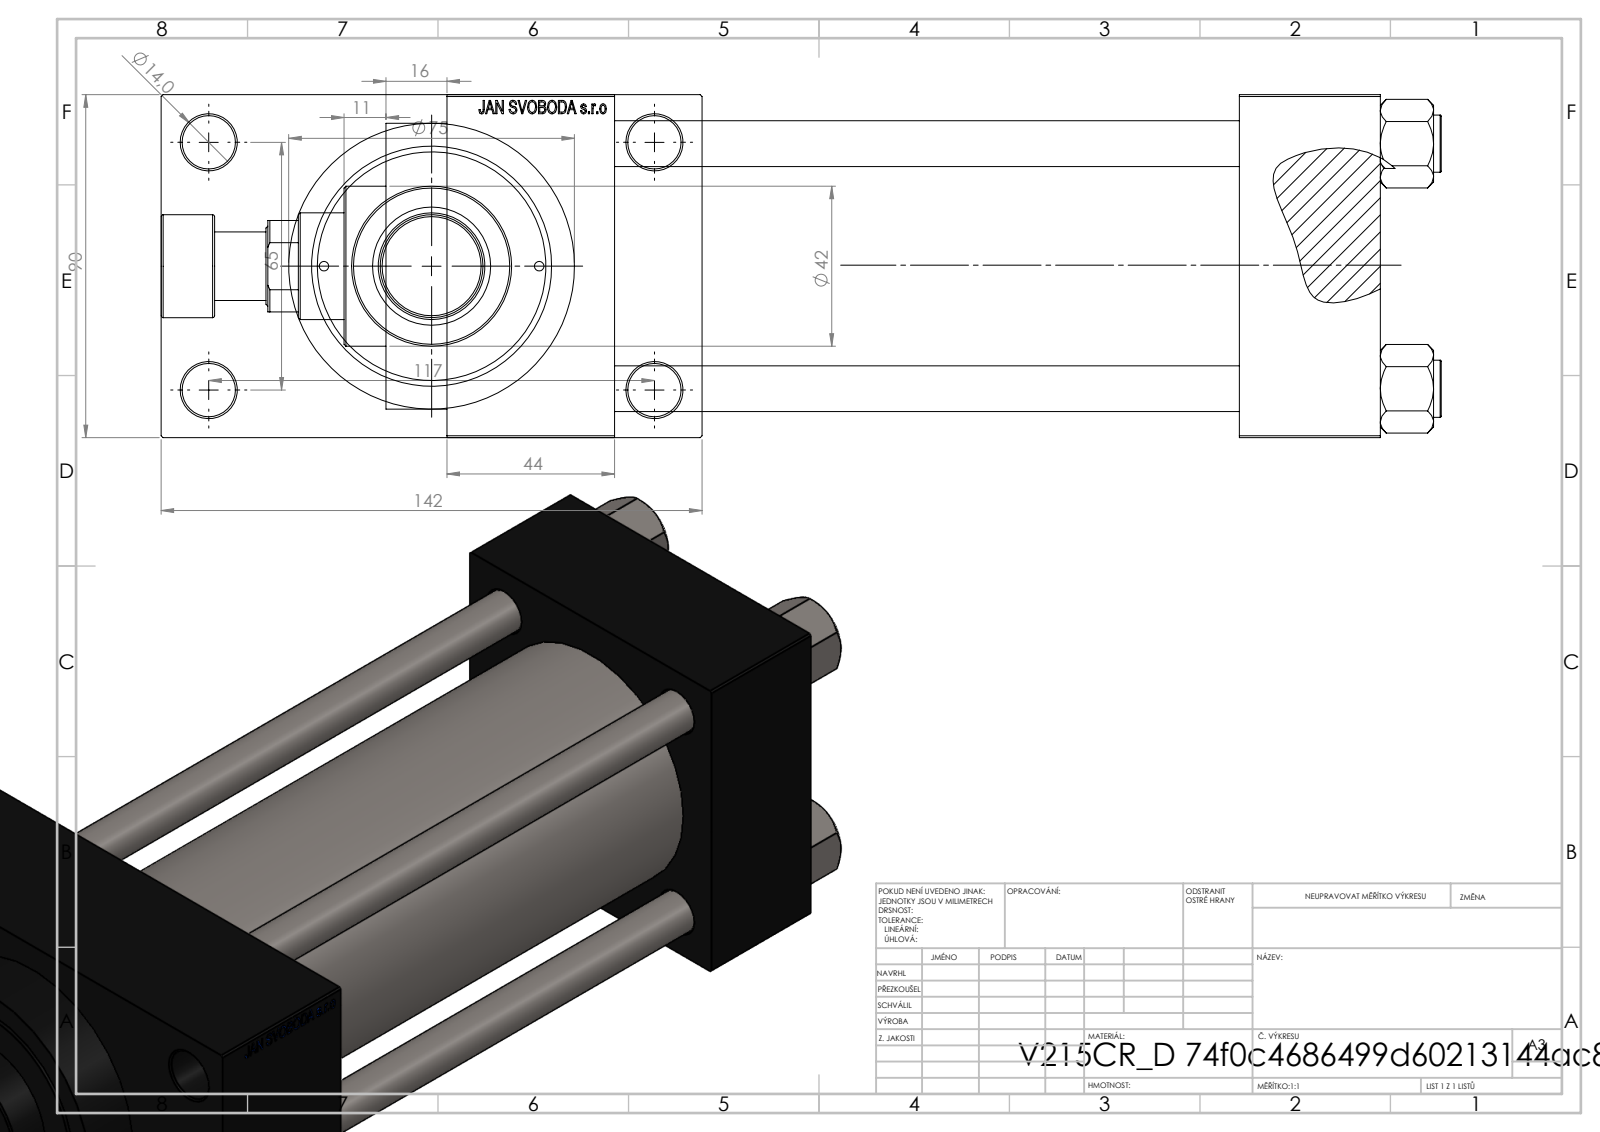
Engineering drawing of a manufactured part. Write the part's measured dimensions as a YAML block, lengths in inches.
part_name: "V215CR_ROD_END_F; V215CR_D_TYCINKA; V215CR_VCP_D; V215_VC_A (+2 more)"
step_written_by: "SolidWorks 2019 (CONFIG_CONTROL_DESIGN)"
units: inches
bodies: {solids: 12, faces: 1125, planar: 503, cylindrical: 96, other: 526}
overall_size: [13.228, 5.591, 3.543]
volume: 78.42
surface_area: 421.8
round_holes:
  - {diameter: 0.472, count: 4}
  - {diameter: 0.551, count: 4}
  - {diameter: 0.098, count: 2}
  - {diameter: 0.276, count: 2}
  - {diameter: 0.825, count: 2}
  - {diameter: 1.181, count: 2}
  - {diameter: 0.728, count: 1}
  - {diameter: 1.102, count: 1}
  - {diameter: 1.22, count: 1}
  - {diameter: 1.969, count: 1}
  - {diameter: 2.362, count: 1}
  - {diameter: 2.48, count: 1}
round_bosses_or_shafts:
  - {diameter: 0.591, count: 4}
  - {diameter: 2.953, count: 1}
  - {diameter: 2.717, count: 1}
  - {diameter: 1.654, count: 1}
  - {diameter: 1.063, count: 1}
  - {diameter: 0.709, count: 1}
face_to_face_distances: [3.543, 6.457, 1.457, 7.913, 8.189, 9.646, 1.732, 1.024, 4.567, 0.63]
hole_center_spacings: [1.037, 1.275, 1.748, 1.79, 2.531, 2.635, 2.694, 2.748]
